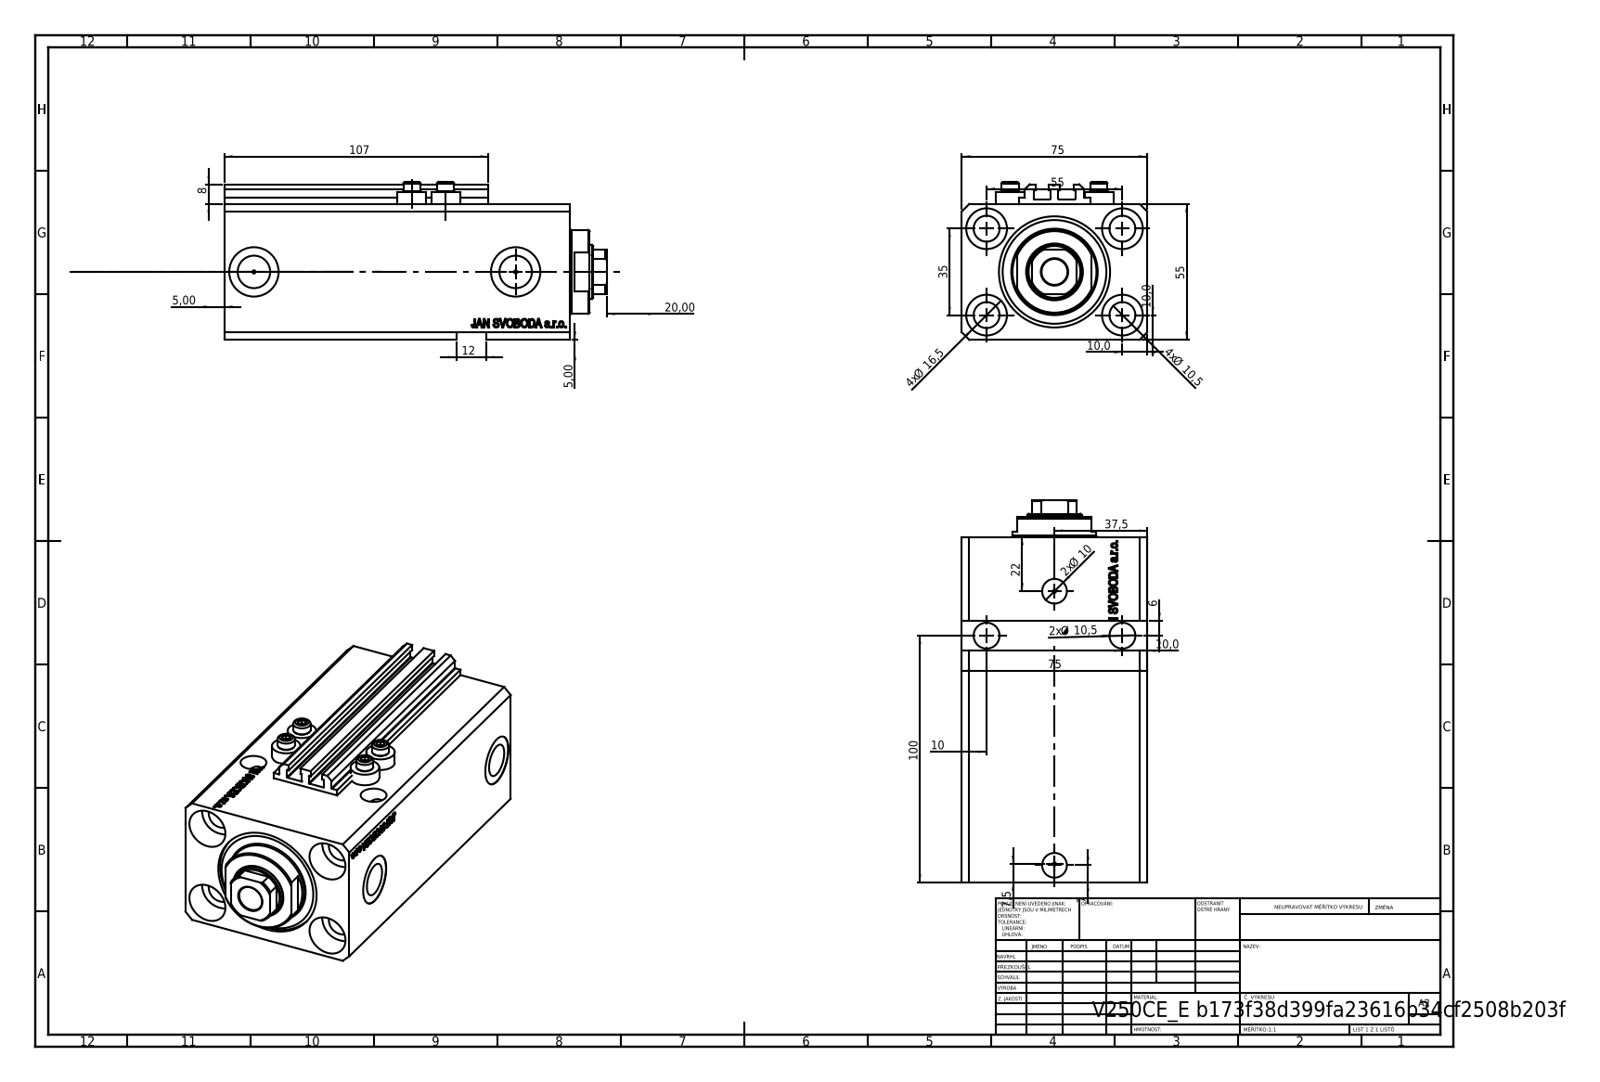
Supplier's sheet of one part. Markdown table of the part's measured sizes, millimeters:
| quantity | value |
| --- | --- |
| part name | V250CE_VC_E; ALLEN BOLT V250CE; V250CE_E; V250CE_C_VCP |
| STEP written by | SolidWorks 2019 (CONFIG_CONTROL_DESIGN) |
| units | millimeters |
| bodies | 8 solids, 1080 faces (518 planar, 138 cylindrical, 424 other) |
| overall size | 154.9 × 75 × 64 |
| volume | 488 023 mm³ |
| surface area | 117 511 mm² |
| round holes (diameter × count) | 10.5 × 7, 1.25 × 4, 4 × 4, 16.5 × 4, 10 × 2, 13.16 × 2, 20 × 2, 22 × 1, 32 × 1, 45 × 1 |
| round bosses / shafts (diameter × count) | 11.6 × 4, 7 × 4, 34 × 1 |
| partial cylindrical surfaces (radius × count) | 0.2 × 10, 10.5 × 1 |
| main face-to-face distances | 55, 75, 9.9, 140, 112.9, 27.1, 3, 57, 103, 130.1 |
| hole center spacings | 32.6, 55, 13.6, 14.09, 25.81, 32.87, 33.62, 35 |
